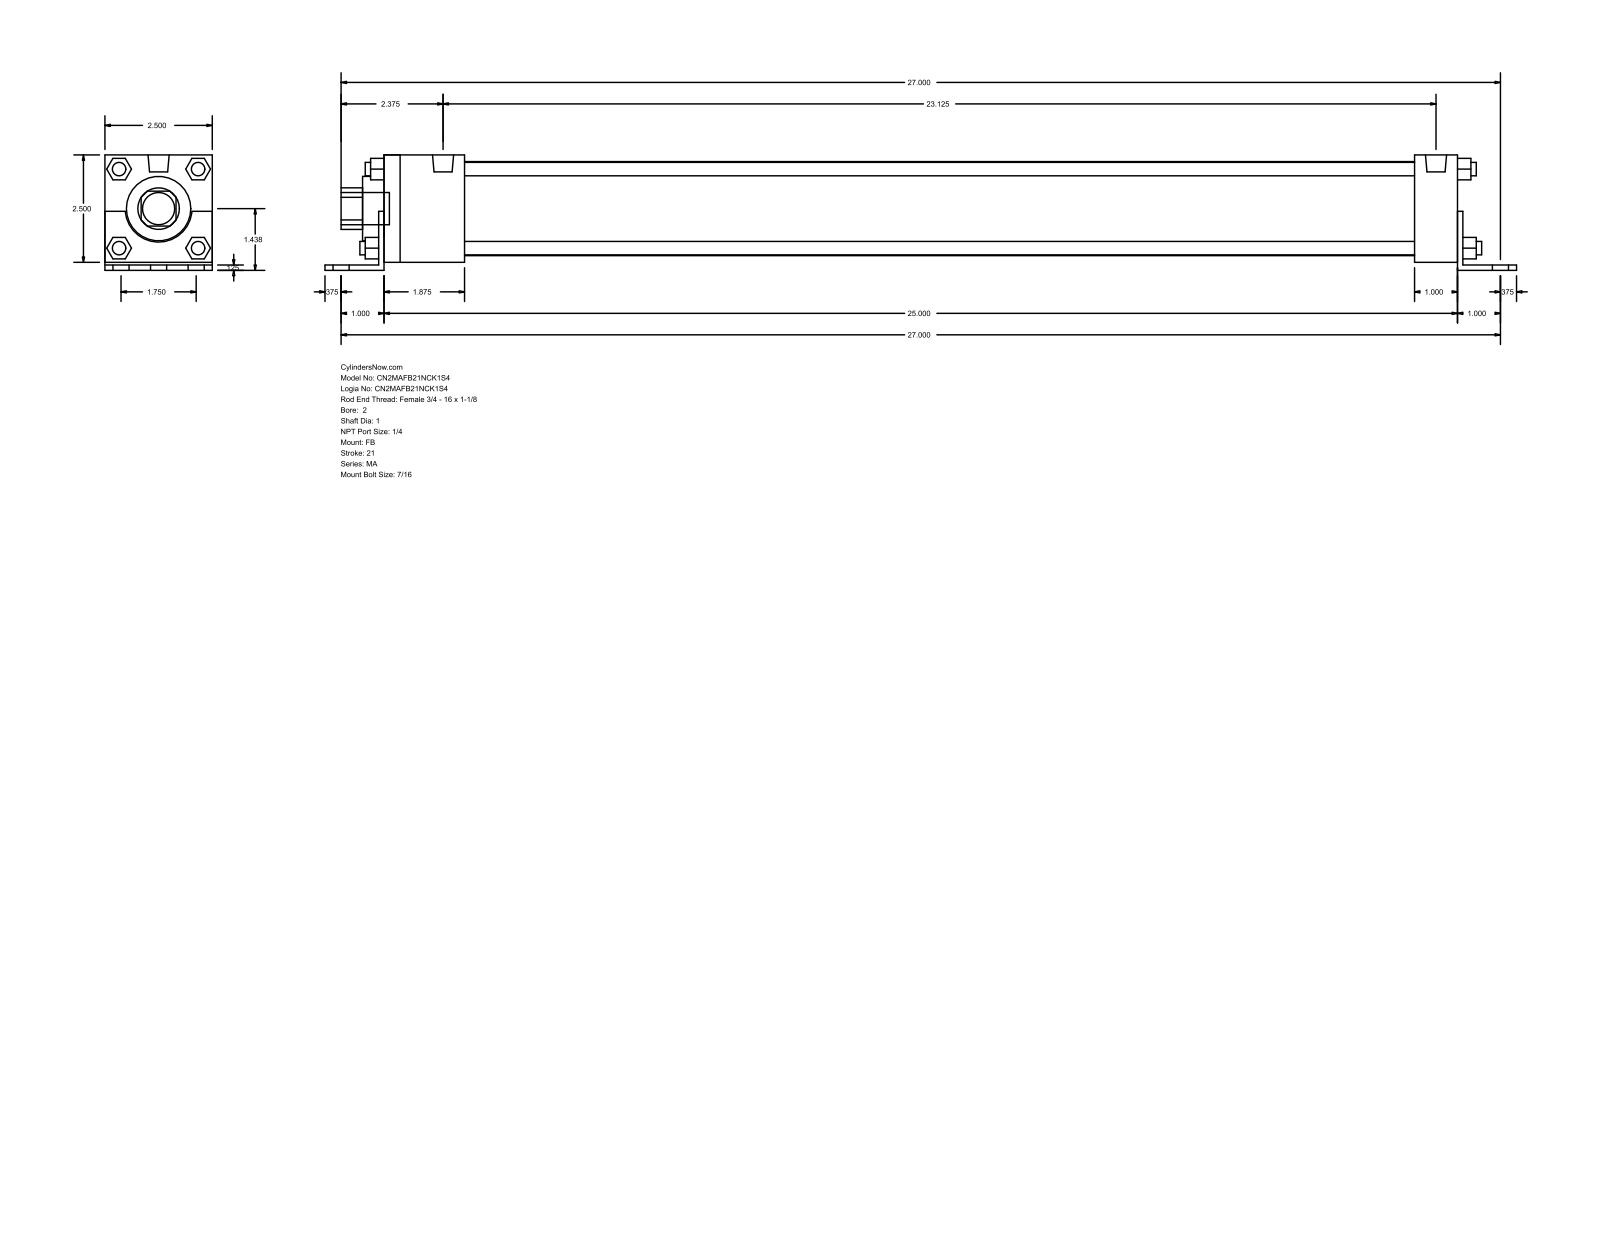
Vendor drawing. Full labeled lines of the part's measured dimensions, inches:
Part name (STEP PRODUCT): MA_FB__0200_1
STEP written by: GSSL Pune (CONFIG_CONTROL_DESIGN)
Units: inches
Bodies: 0 solids, 140 faces (105 planar, 35 cylindrical, 0 other)
Overall size (bounding box): 27.75 × 2.687 × 2.5
Round holes (diameter × count): ⌀1 ×1, ⌀1.5 ×1, ⌀2.19 ×1
Round bosses / shafts (diameter × count): ⌀0.313 ×8, ⌀0.437 ×6, ⌀0.492 ×2, ⌀0.75 ×1
Partial cylindrical surfaces — rounded edges, fillets, slot ends (radius × count): R0.484 ×1, R0.78 ×1
Main face-to-face distances: 2.5, 0.125, 0.187, 2.687, 0.063, 2.563, 0.5, 0.125, 25, 25.125
